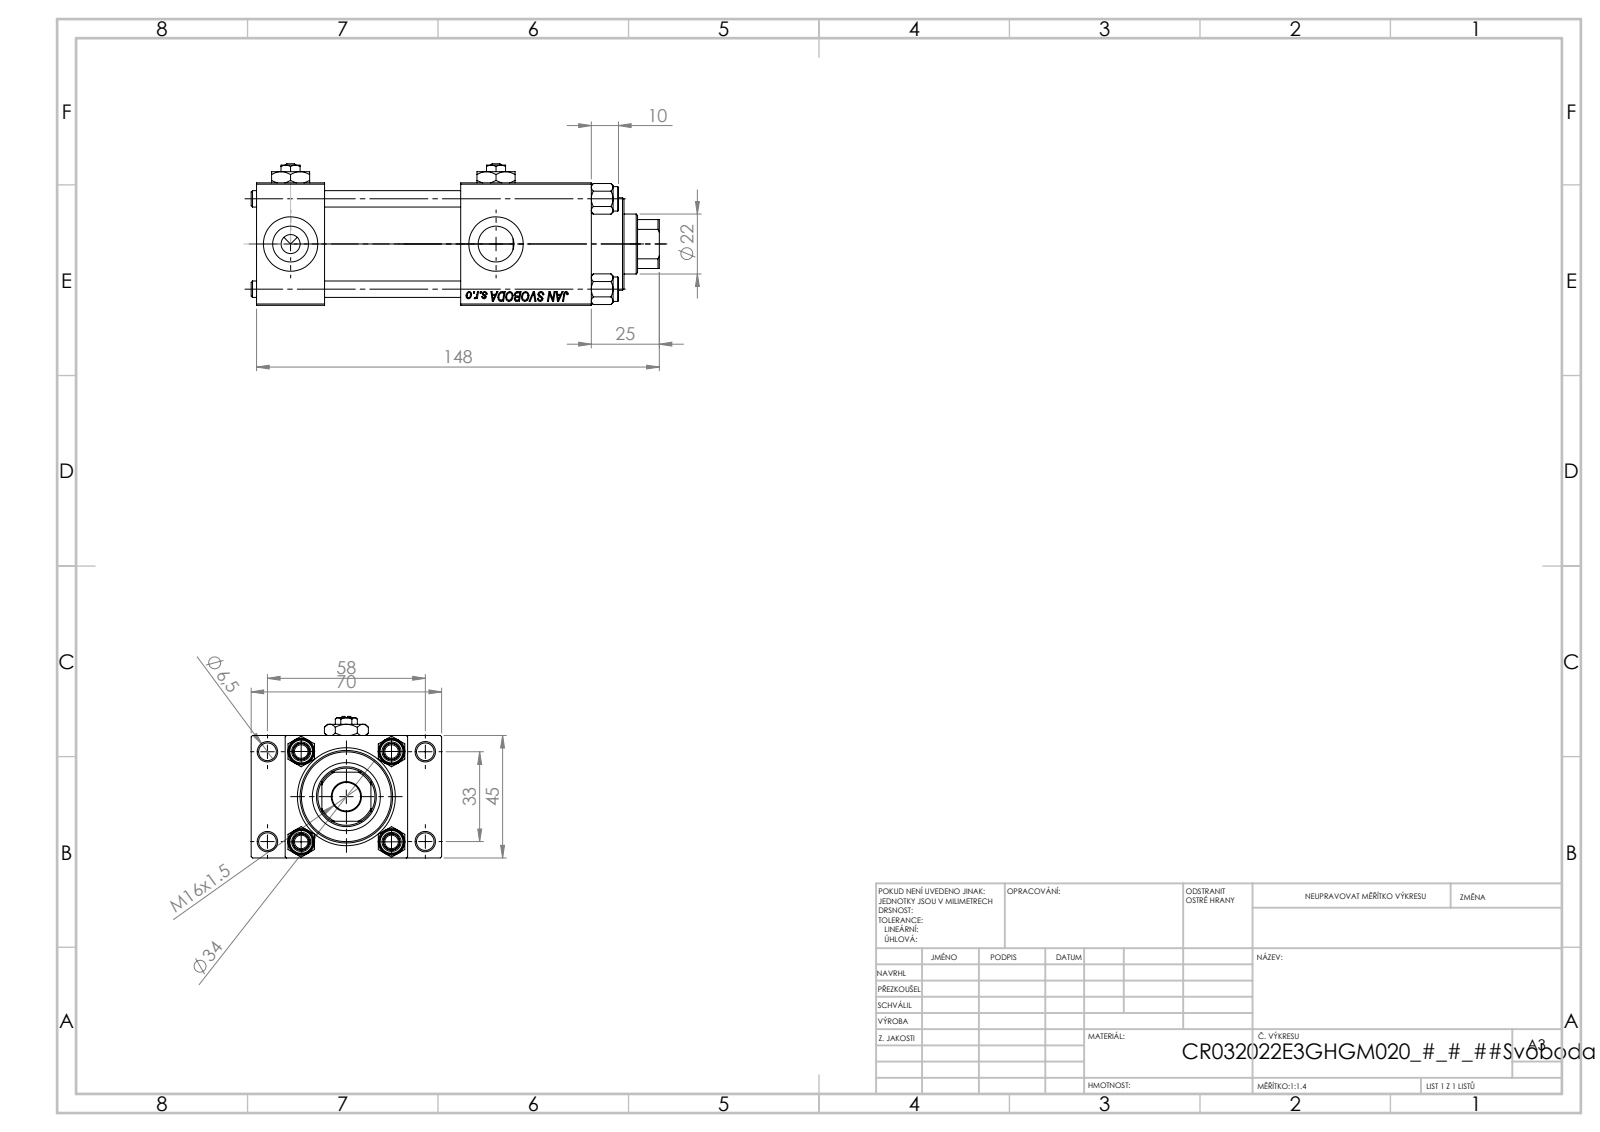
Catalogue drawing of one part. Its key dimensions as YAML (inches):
part_name: "V215CR_E_Body; V215CR_VCP_E; Zatka_pro_OIL_PORT; V215_VC_A (+2 more)"
step_written_by: "SolidWorks 2019 (CONFIG_CONTROL_DESIGN)"
units: inches
bodies: {solids: 13, faces: 1235, planar: 544, cylindrical: 97, other: 594}
overall_size: [5.906, 2.756, 2.047]
volume: 14.29
surface_area: 128.3
round_holes:
  - {diameter: 0.236, count: 4}
  - {diameter: 0.256, count: 4}
  - {diameter: 0.518, count: 4}
  - {diameter: 0.787, count: 4}
  - {diameter: 0.276, count: 3}
  - {diameter: 0.413, count: 1}
  - {diameter: 0.866, count: 1}
  - {diameter: 0.945, count: 1}
  - {diameter: 0.984, count: 1}
  - {diameter: 1.26, count: 1}
  - {diameter: 1.299, count: 1}
round_bosses_or_shafts:
  - {diameter: 0.354, count: 4}
  - {diameter: 1.496, count: 1}
  - {diameter: 1.339, count: 1}
partial_cylinders:
  - {radius: 0.413, count: 1}
face_to_face_distances: [1.772, 0.984, 0.492, 2.264, 4.843, 1.969, 2.953, 3.858, 1.89, 2.756]
hole_center_spacings: [0.488, 0.924, 1.307, 1.314, 1.392, 1.795, 2.219, 1.299]
